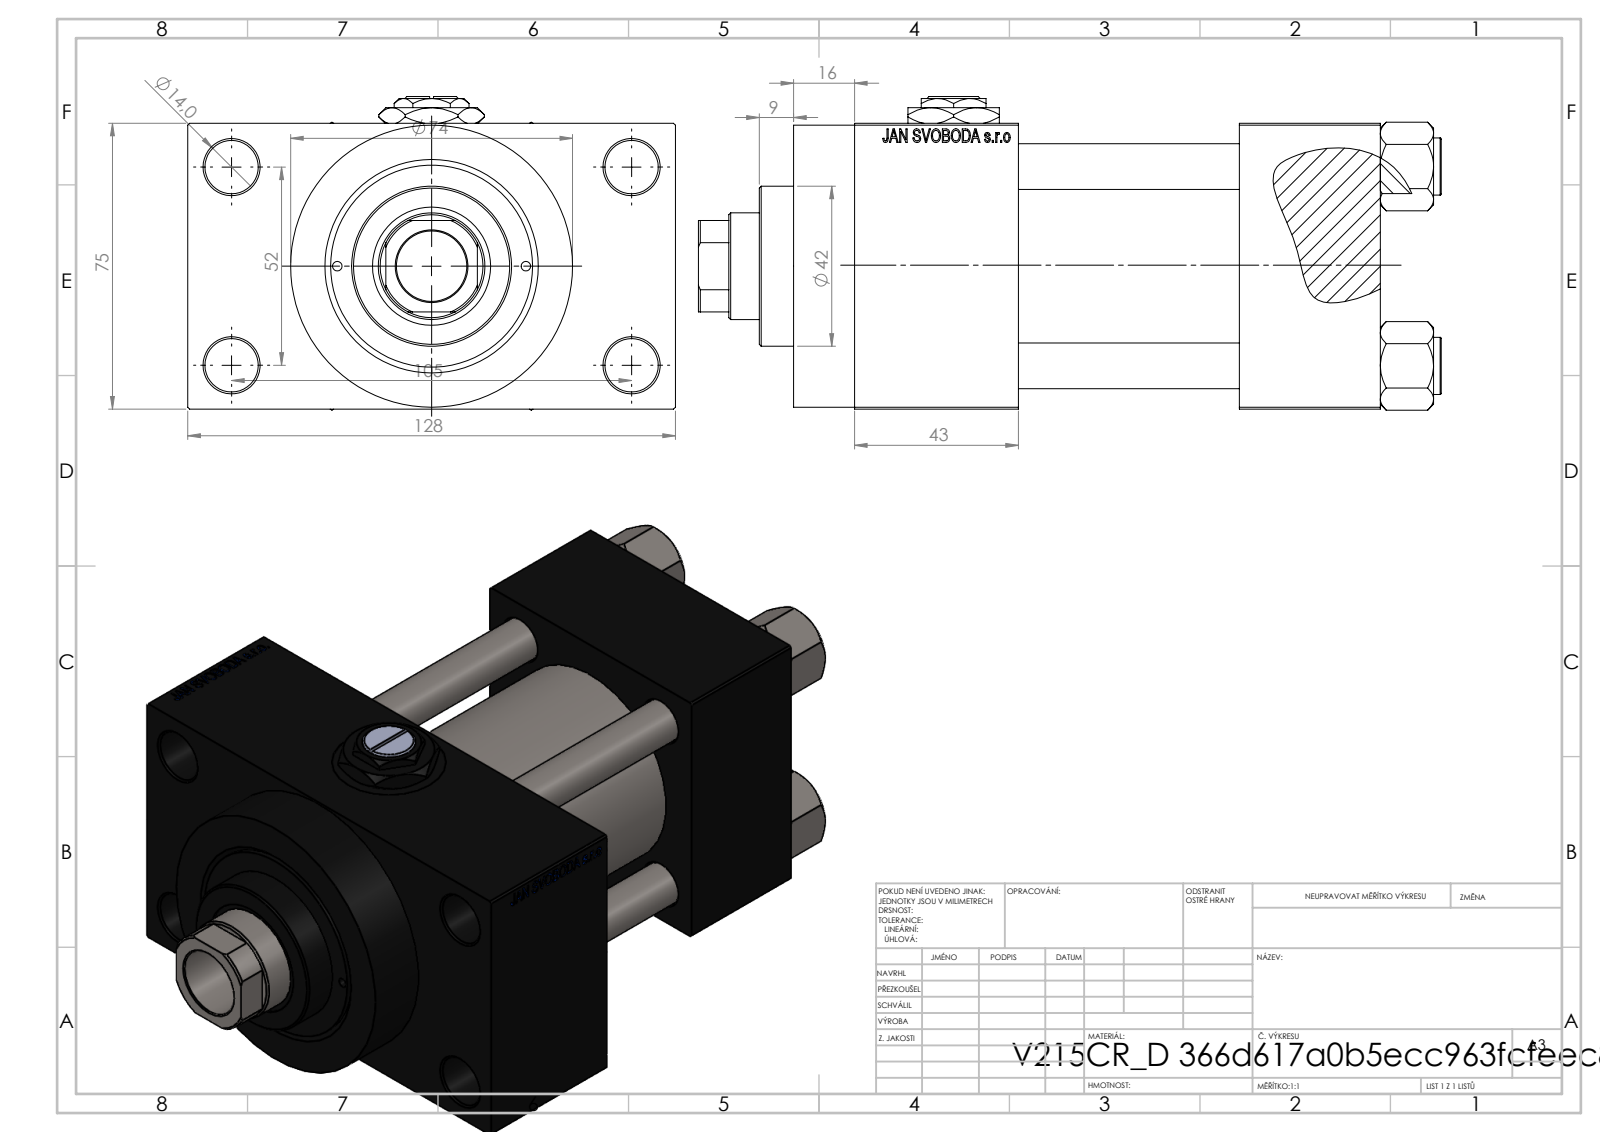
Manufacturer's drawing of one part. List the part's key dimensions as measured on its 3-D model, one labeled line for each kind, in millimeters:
Part name (STEP PRODUCT): V215_VC_A; V215CR_D_TYCINKA; V215CR_VCP_D; V215CR_D_Body (+2 more)
STEP written by: SolidWorks 2019 (CONFIG_CONTROL_DESIGN)
Units: millimetres
Bodies: 12 solids, 1159 faces (523 planar, 96 cylindrical, 540 other)
Overall size (bounding box): 195 × 128 × 82.27
Volume: 803 755 mm³ · Surface area: 172 171 mm²
Round holes (diameter × count): ⌀12 ×4, ⌀14 ×4, ⌀20.96 ×3, ⌀30 ×3, ⌀2.5 ×2, ⌀7 ×2, ⌀18.5 ×1, ⌀28 ×1, ⌀31 ×1, ⌀41 ×1, ⌀50 ×1, ⌀53 ×1
Round bosses / shafts (diameter × count): ⌀15 ×4, ⌀74 ×1, ⌀56 ×1, ⌀42 ×1
Partial cylindrical surfaces — rounded edges, fillets, slot ends (radius × count): R13.5 ×1
Main face-to-face distances: 75, 58, 37, 95, 26.5, 138, 101, 43, 101.5, 16
Hole centre spacings: 26.19, 26.35, 36.98, 38.03, 52.3, 57.22, 58.43, 58.59
